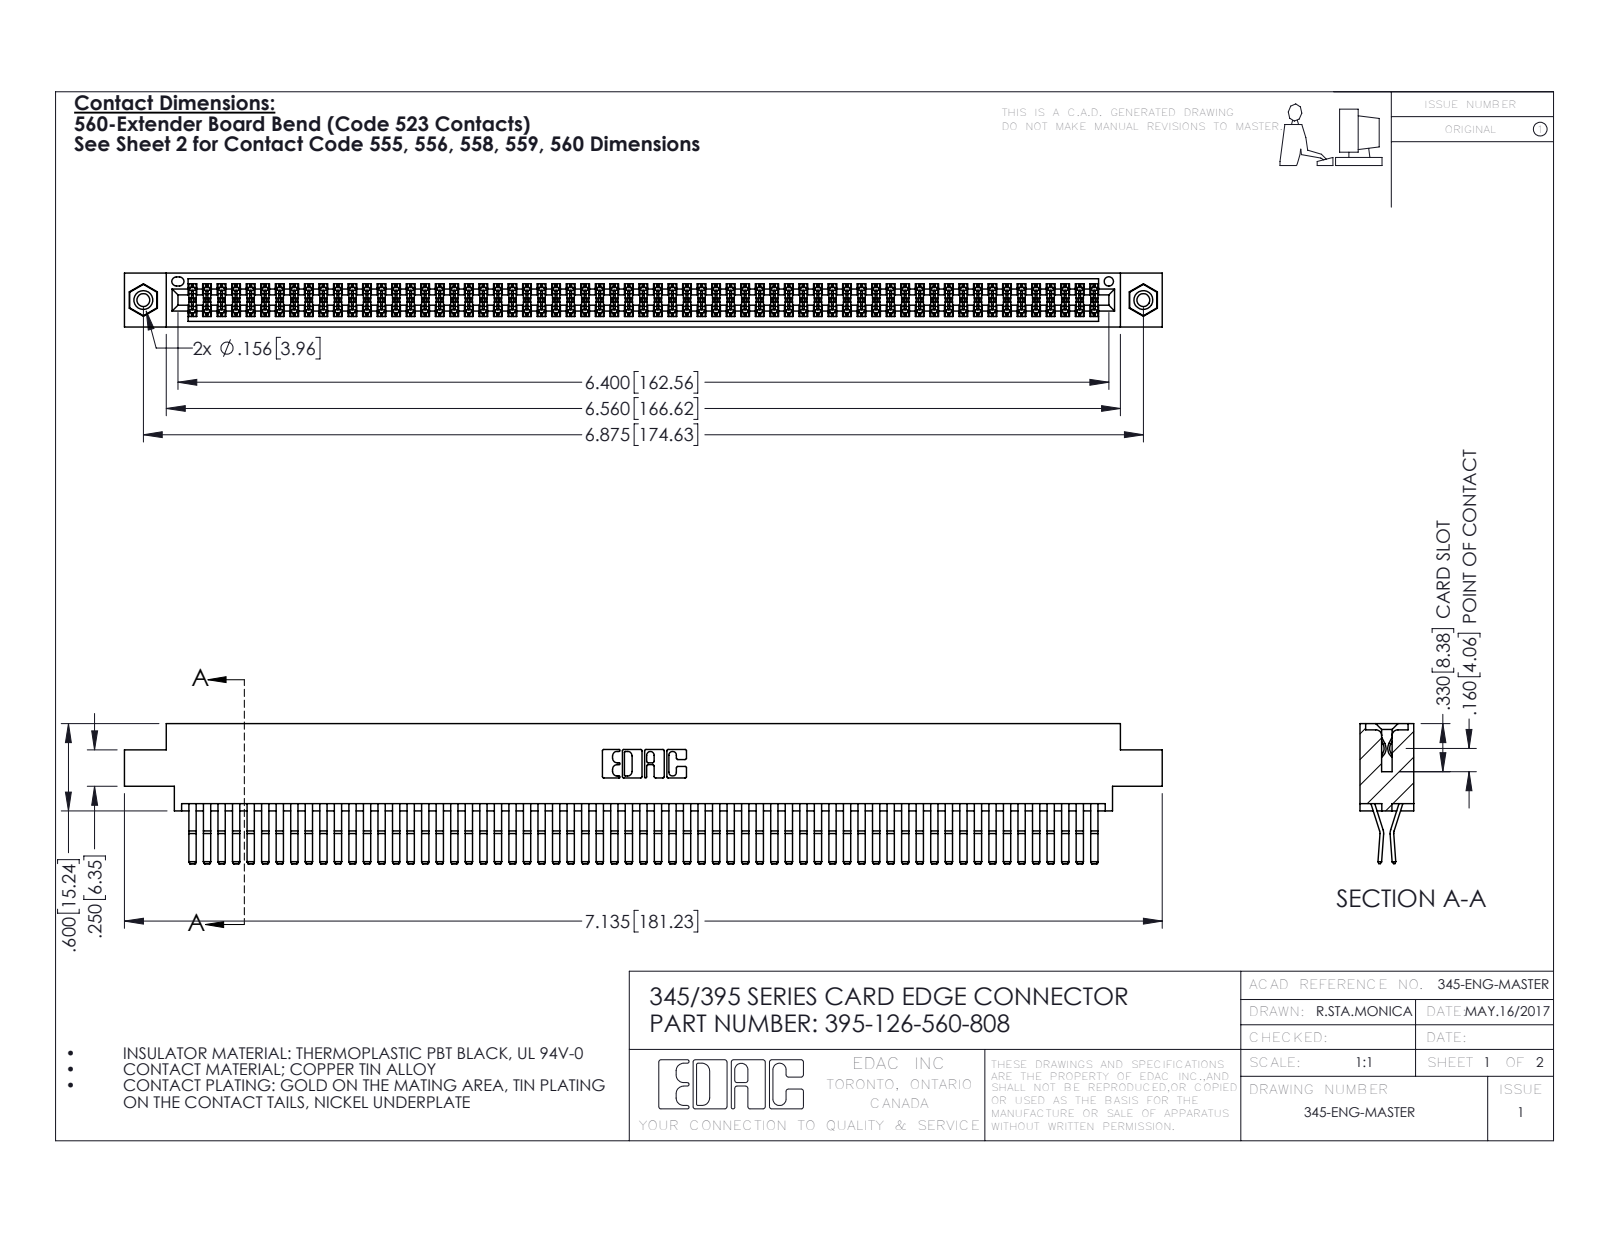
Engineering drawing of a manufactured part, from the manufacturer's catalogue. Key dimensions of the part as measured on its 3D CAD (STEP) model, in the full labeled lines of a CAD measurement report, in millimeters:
Part name (STEP PRODUCT): 345-292-001_560 Tail; 345-250-001_345-250-003-102; 345 Part_0.170 Offset - 0.156 Dia-TI; 395-126-560-808
STEP written by: SolidWorks 2016 (CONFIG_CONTROL_DESIGN)
Units: millimetres
Bodies: 129 solids, 6742 faces (4274 planar, 2452 cylindrical, 16 other)
Overall size (bounding box): 181.2 × 24.4 × 9.4
Volume: 18 500 mm³ · Surface area: 30 050 mm²
Round holes (diameter × count): ⌀2.3 ×2, ⌀3.2 ×2, ⌀4 ×2, ⌀1.6 ×1
Round bosses / shafts (diameter × count): ⌀3.9 ×2
Partial cylindrical surfaces — rounded edges, fillets, slot ends (radius × count): R0.2 ×190, R0.3 ×22, R0.2 ×6, R0.8 ×6, R0.7 ×3, R0.3 ×2, R0.4 ×2, R0.5 ×2
Main face-to-face distances: 0.6, 1.8, 7.6, 9.4, 5.1, 2.5, 6.9, 5.7, 4.4, 3.8
Hole centre spacings: 6.9, 168.6, 174.6
